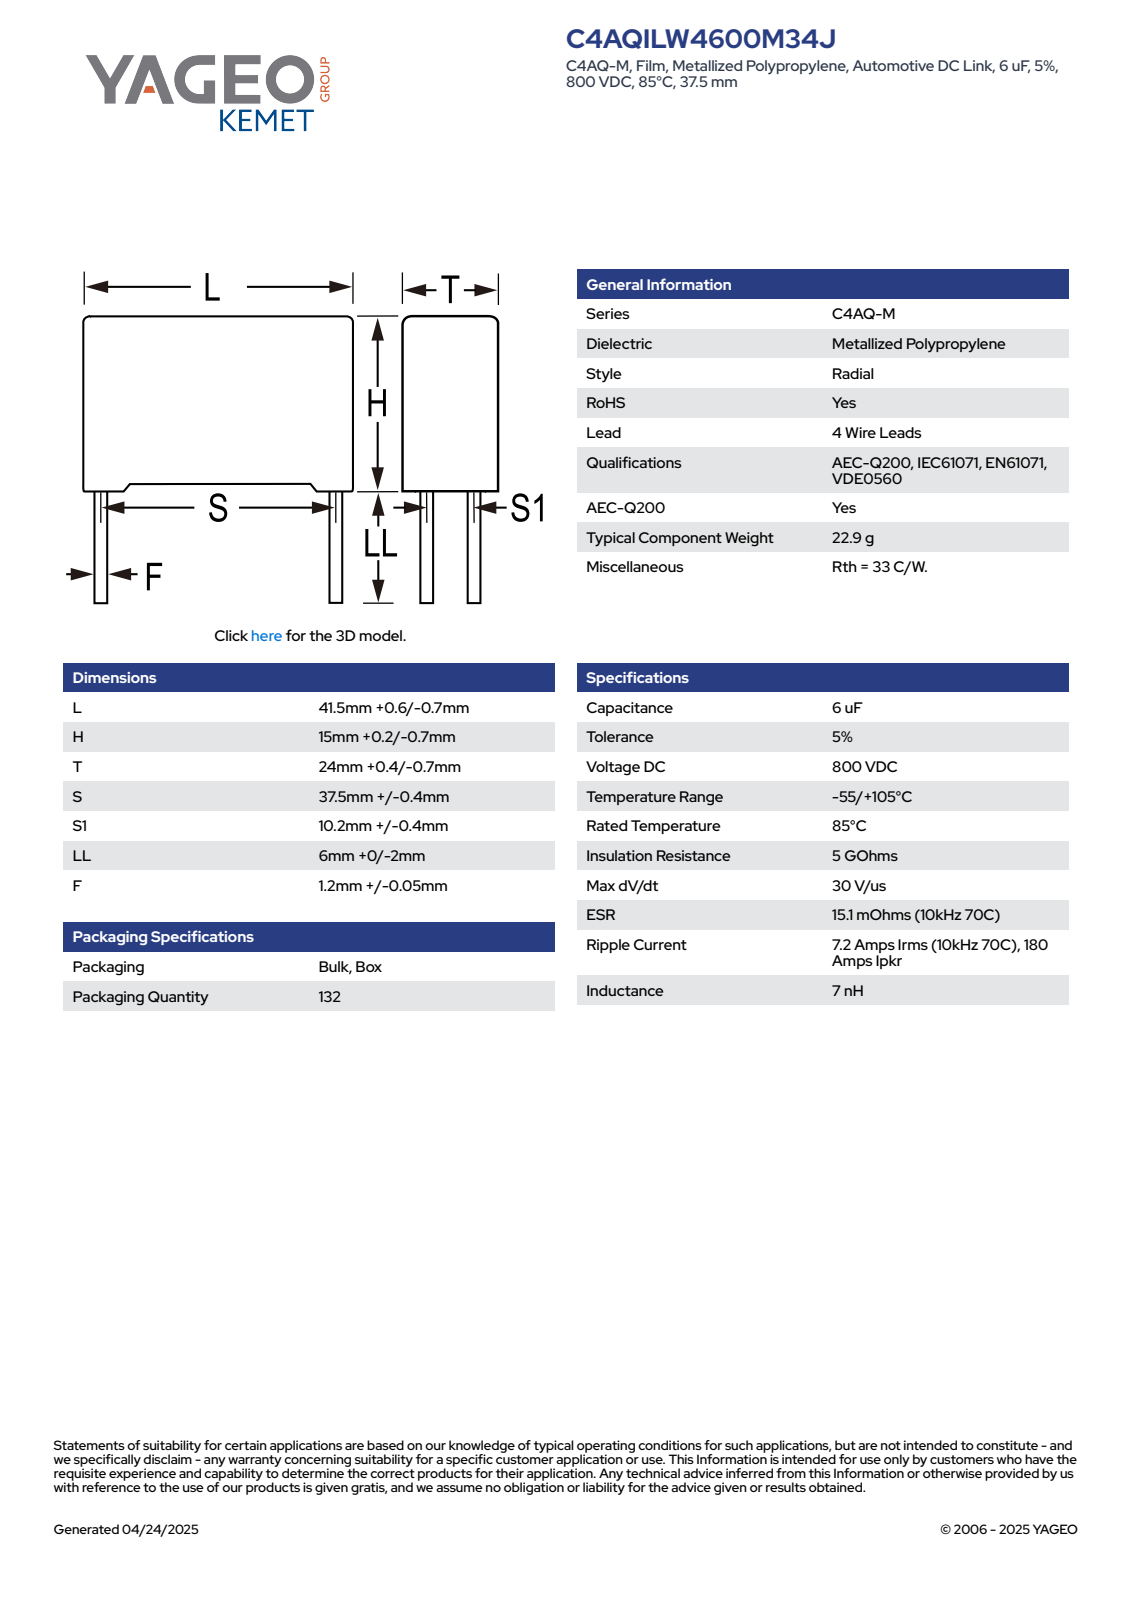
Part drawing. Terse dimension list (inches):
name: CFP_RB4_41.5X15X24_L42.1H15.2T24.4S37.5S110.2LL6F1.25
written by: SolidWorks 2014 (AUTOMOTIVE_DESIGN)
unit: in
bodies: 4 solids, 87 faces (79 planar, 8 cylindrical, 0 other)
size: 1.657 × 0.961 × 0.835
volume: 0.93 in³; area: 6.66 in²
bosses: 4× ⌀0.049
face distances: 0.581, 0.961, 1.657, 0.018, 0.598, 0.961, 0.059, 1.598, 0.902, 1.539
